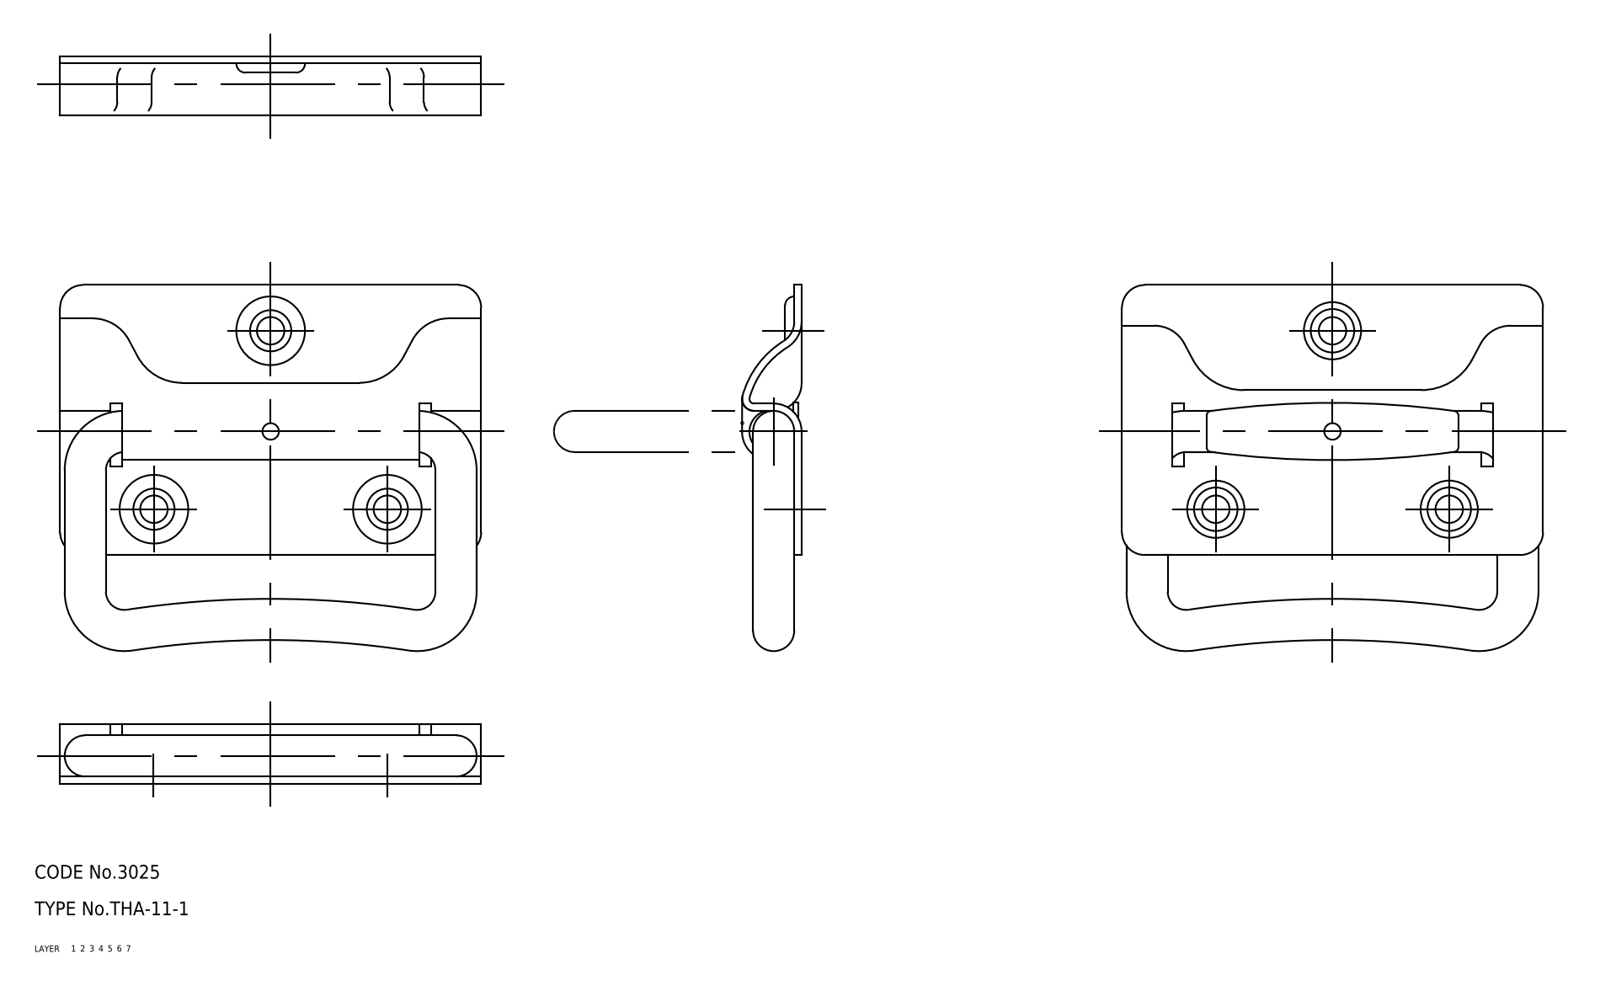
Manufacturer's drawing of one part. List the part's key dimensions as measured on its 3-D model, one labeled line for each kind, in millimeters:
Part name (STEP PRODUCT): pin; leaf spring; grip; base (+1 more)
STEP written by: CADfix (AUTOMOTIVE_DESIGN)
Units: millimetres
Bodies: 4 solids, 176 faces (0 planar, 0 cylindrical, 176 other)
Overall size (bounding box): 92 × 80.01 × 13
Volume: 24 833 mm³ · Surface area: 21 388 mm²
